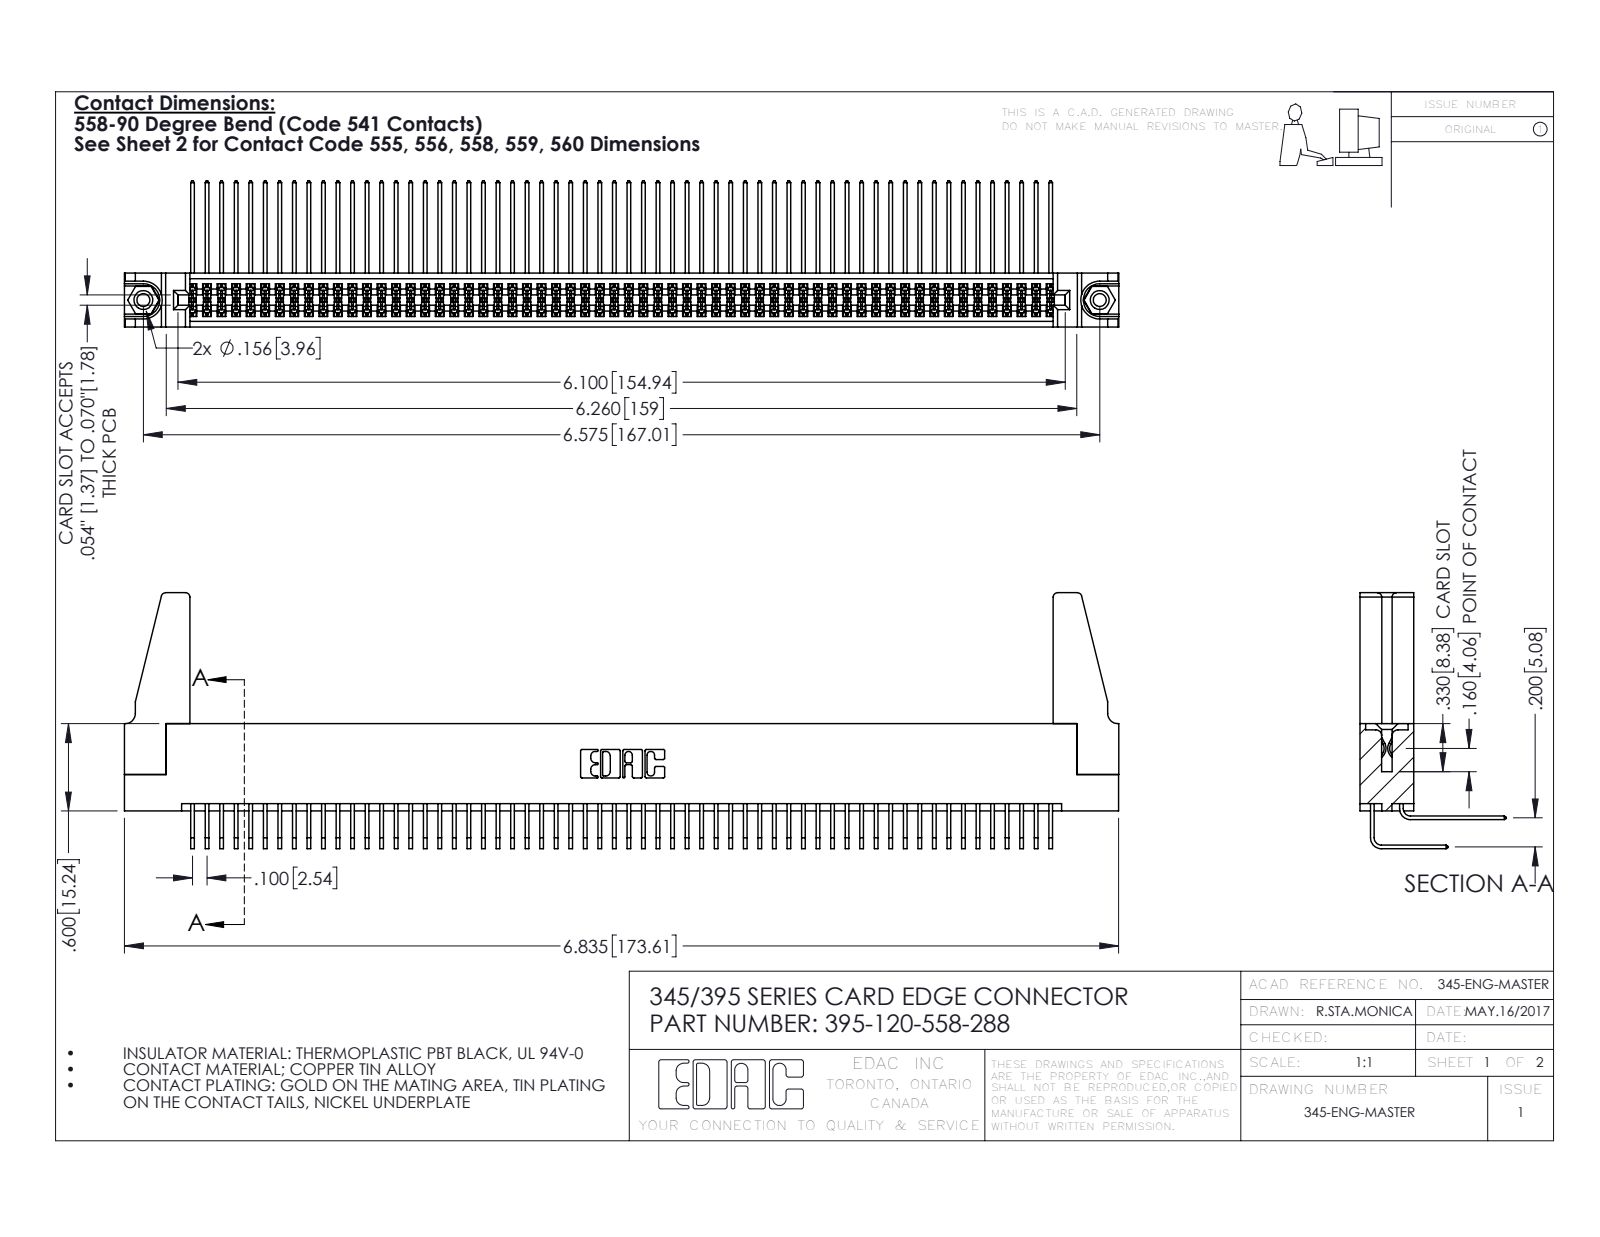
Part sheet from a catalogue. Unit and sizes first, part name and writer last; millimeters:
Units: millimetres
Overall size (bounding box): 173.6 × 44.7 × 25.5
Round holes (diameter × count): ⌀2.3 ×2, ⌀3.2 ×2, ⌀4 ×2, ⌀1.6 ×1
Round bosses / shafts (diameter × count): ⌀3.9 ×2
Partial cylindrical surfaces — rounded edges, fillets, slot ends (radius × count): R0.2 ×181, R0.3 ×22, R0.8 ×8, R0.2 ×6, R0.8 ×6, R0.7 ×3, R0.4 ×2, R0.5 ×2
Main face-to-face distances: 1.8, 7.6, 5.1, 9.4, 2.5, 6.9, 0.6, 5.7, 0.6, 7.2
Hole centre spacings: 6.9, 161, 167
Volume: 20 980 mm³ · Surface area: 32 930 mm²
Bodies: 125 solids, 6490 faces (4352 planar, 2122 cylindrical, 16 other)
Part name (STEP PRODUCT): 345-292-001_558 559 Tail - 1; 345-250-001_345-250-001-102; 345-292-001_558 Tail - 2; 345-220-078_345-220-088 (+2 more)
STEP written by: SolidWorks 2016 (CONFIG_CONTROL_DESIGN)
